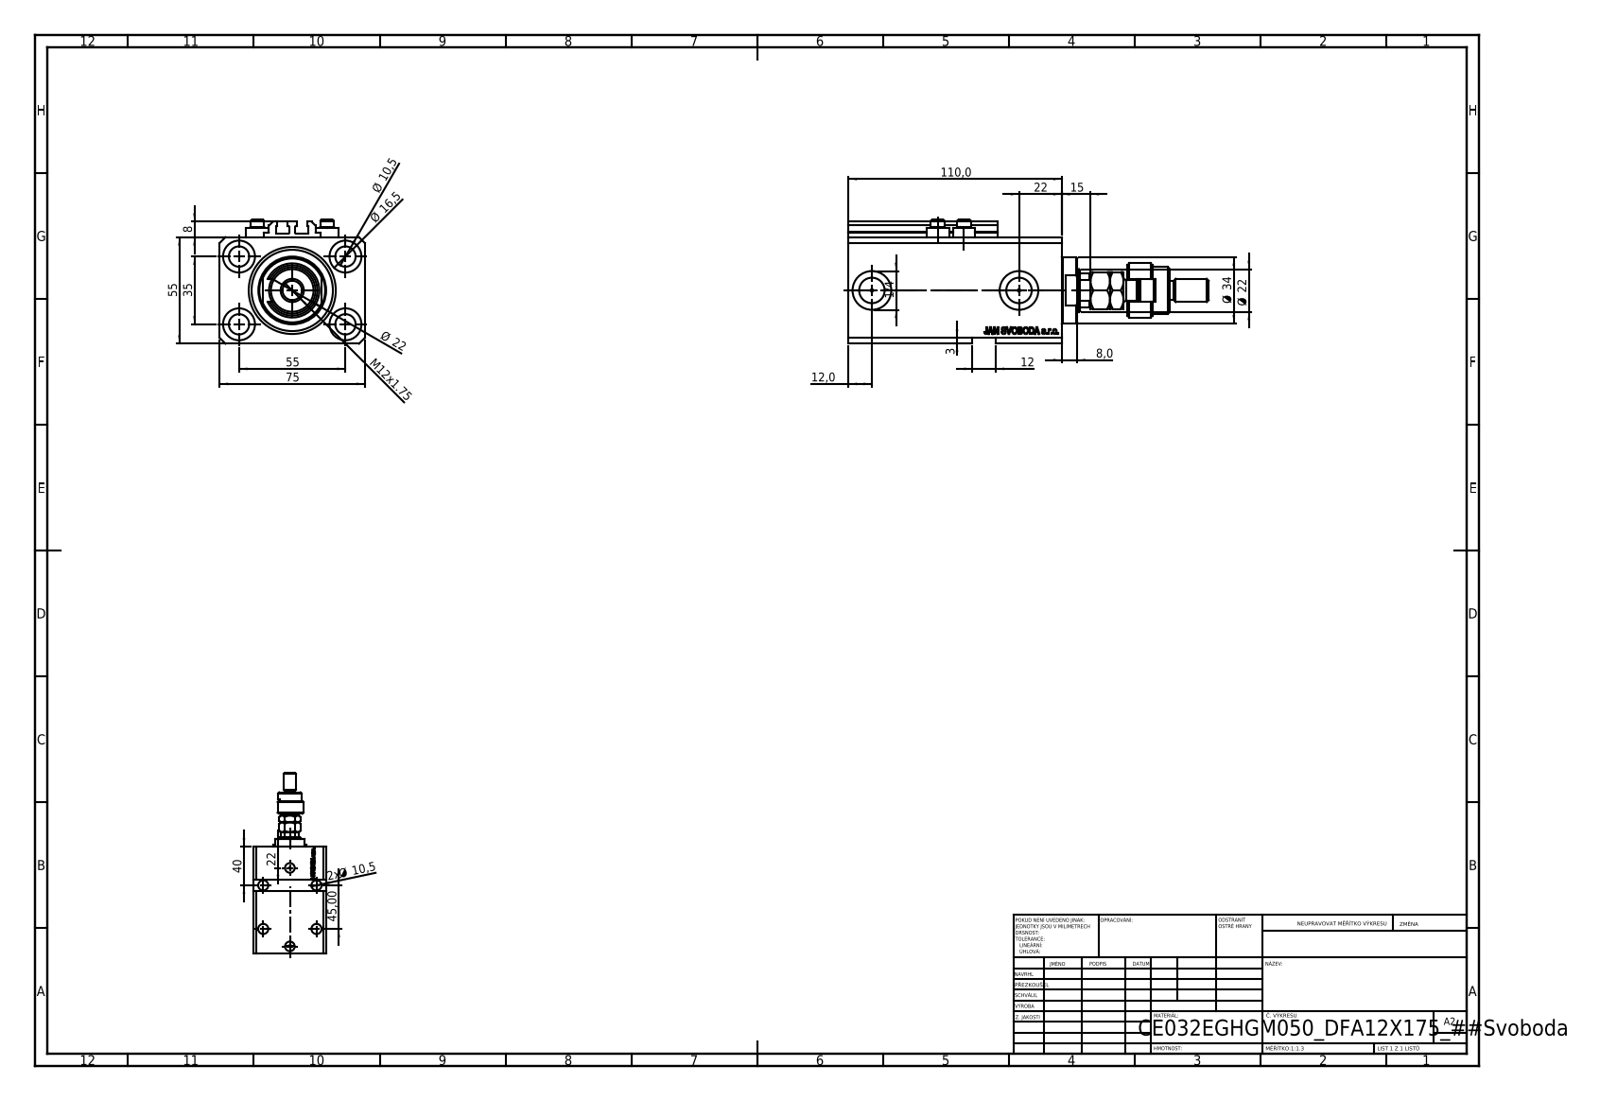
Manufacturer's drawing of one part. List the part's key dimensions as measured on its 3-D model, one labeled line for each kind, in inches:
Part name (STEP PRODUCT): MFA; ALLEN BOLT V250CE; FEMALE_PART_FOR_DFA; V250CE_C_VCP (+2 more)
STEP written by: SolidWorks 2019 (CONFIG_CONTROL_DESIGN)
Units: inches
Bodies: 10 solids, 1169 faces (542 planar, 159 cylindrical, 468 other)
Overall size (bounding box): 7.323 × 2.953 × 2.52
Volume: 24.36 in³ · Surface area: 159.3 in²
Round holes (diameter × count): ⌀0.413 ×9, ⌀0.049 ×4, ⌀0.157 ×4, ⌀0.65 ×4, ⌀0.394 ×2, ⌀0.518 ×2, ⌀0.787 ×2, ⌀0.866 ×1, ⌀1.26 ×1, ⌀1.772 ×1
Round bosses / shafts (diameter × count): ⌀0.457 ×4, ⌀0.276 ×4, ⌀1.339 ×1, ⌀1.102 ×1, ⌀0.945 ×1, ⌀0.709 ×1, ⌀0.472 ×1, ⌀0.433 ×1
Partial cylindrical surfaces — rounded edges, fillets, slot ends (radius × count): R0.008 ×10, R0.384 ×1, R0.413 ×1
Main face-to-face distances: 2.165, 2.953, 0.591, 4.331, 0.118, 3.74, 0.39, 0.315, 0.748, 3.35
Hole centre spacings: 1.283, 1.294, 2.165, 2.706, 0.535, 0.555, 0.907, 1.016
